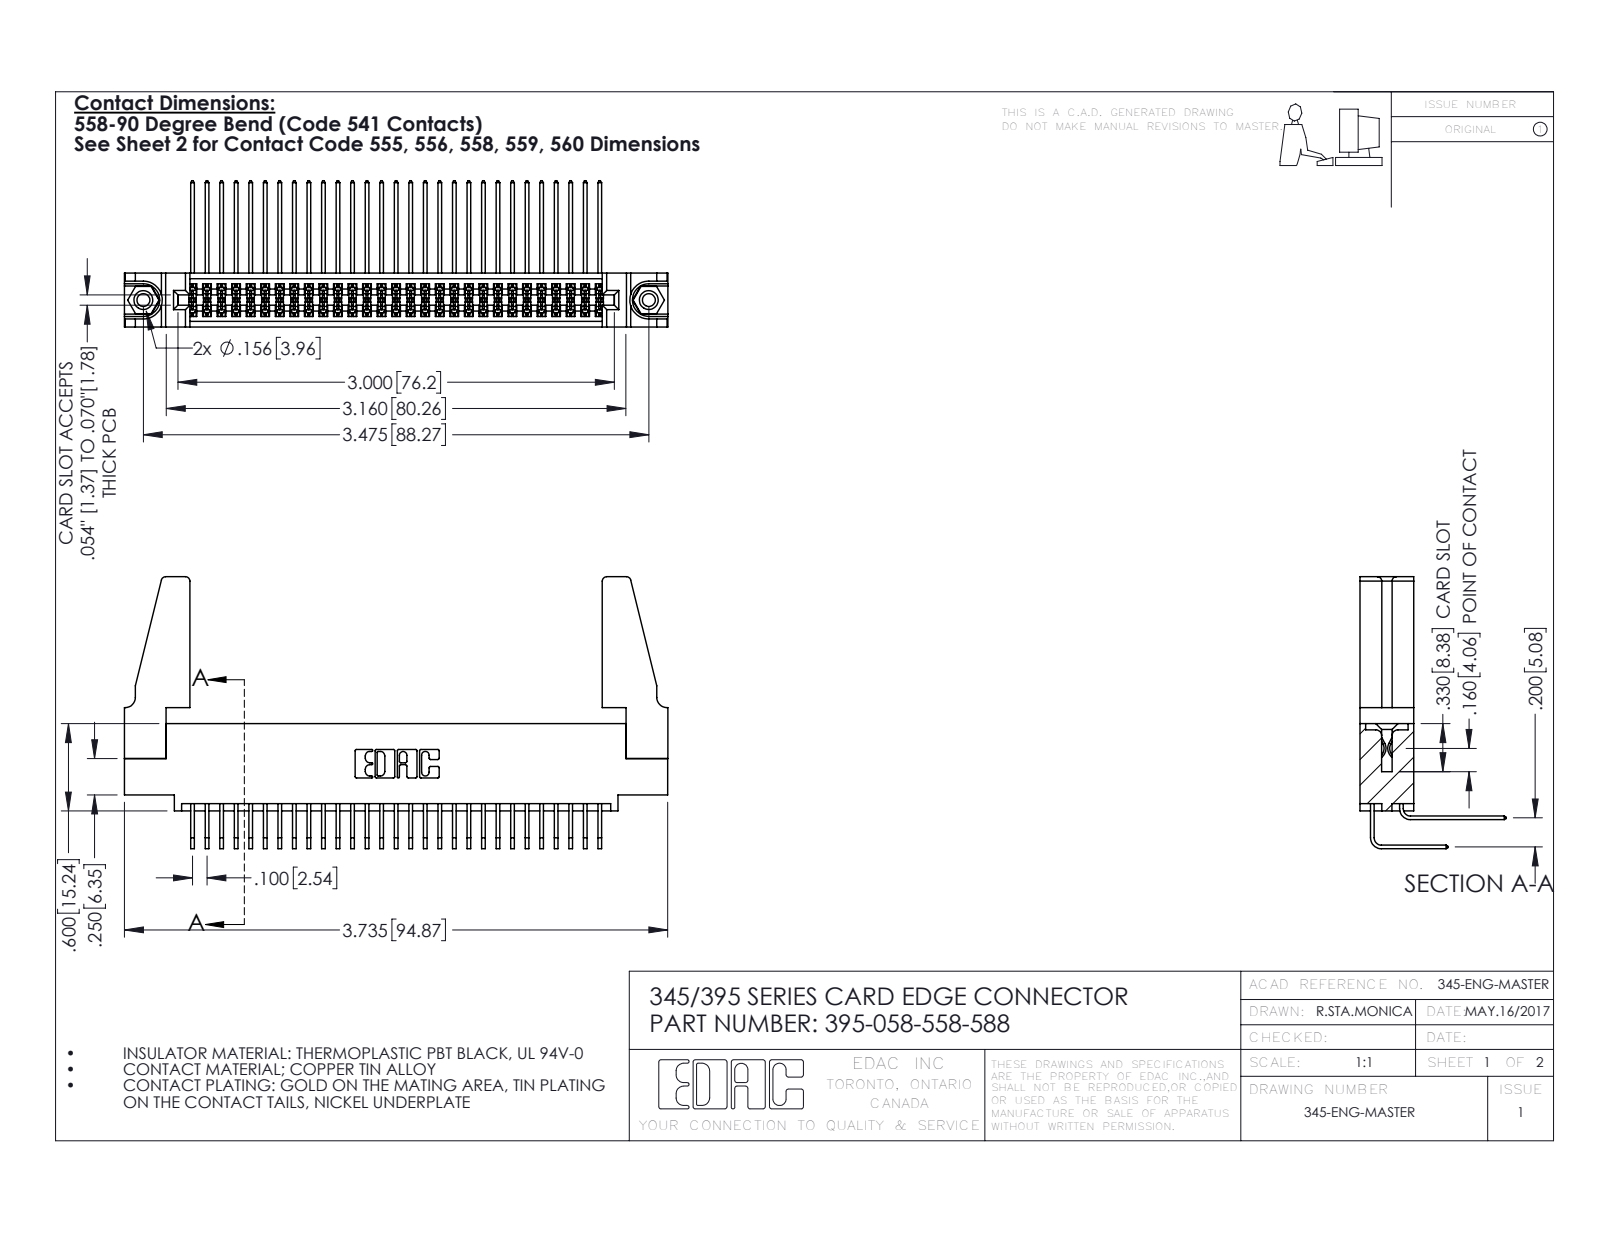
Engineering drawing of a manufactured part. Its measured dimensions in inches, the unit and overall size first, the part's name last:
Units: inches
Overall size (bounding box): 3.736 × 1.869 × 1.005
Round holes (diameter × count): ⌀0.089 ×2, ⌀0.125 ×2, ⌀0.156 ×2, ⌀0.064 ×1
Round bosses / shafts (diameter × count): ⌀0.155 ×2
Partial cylindrical surfaces — rounded edges, fillets, slot ends (radius × count): R0.006 ×88, R0.01 ×22, R0.03 ×8, R0.007 ×6, R0.031 ×6, R0.026 ×3, R0.014 ×2, R0.019 ×2
Main face-to-face distances: 0.072, 0.298, 0.37, 0.2, 0.098, 0.272, 0.025, 0.225, 0.025, 0.175
Hole centre spacings: 0.27, 3.24, 3.475
Volume: 0.77 in³ · Surface area: 28.47 in²
Bodies: 63 solids, 3270 faces (2186 planar, 1068 cylindrical, 16 other)
Part name (STEP PRODUCT): 345-292-001_558 559 Tail - 1; 395-058-558-588; 345-250-001_345-250-001-102; 345 Part_0.110 Offset - 0.156 Dia-TH (+2 more)
STEP written by: SolidWorks 2016 (CONFIG_CONTROL_DESIGN)
